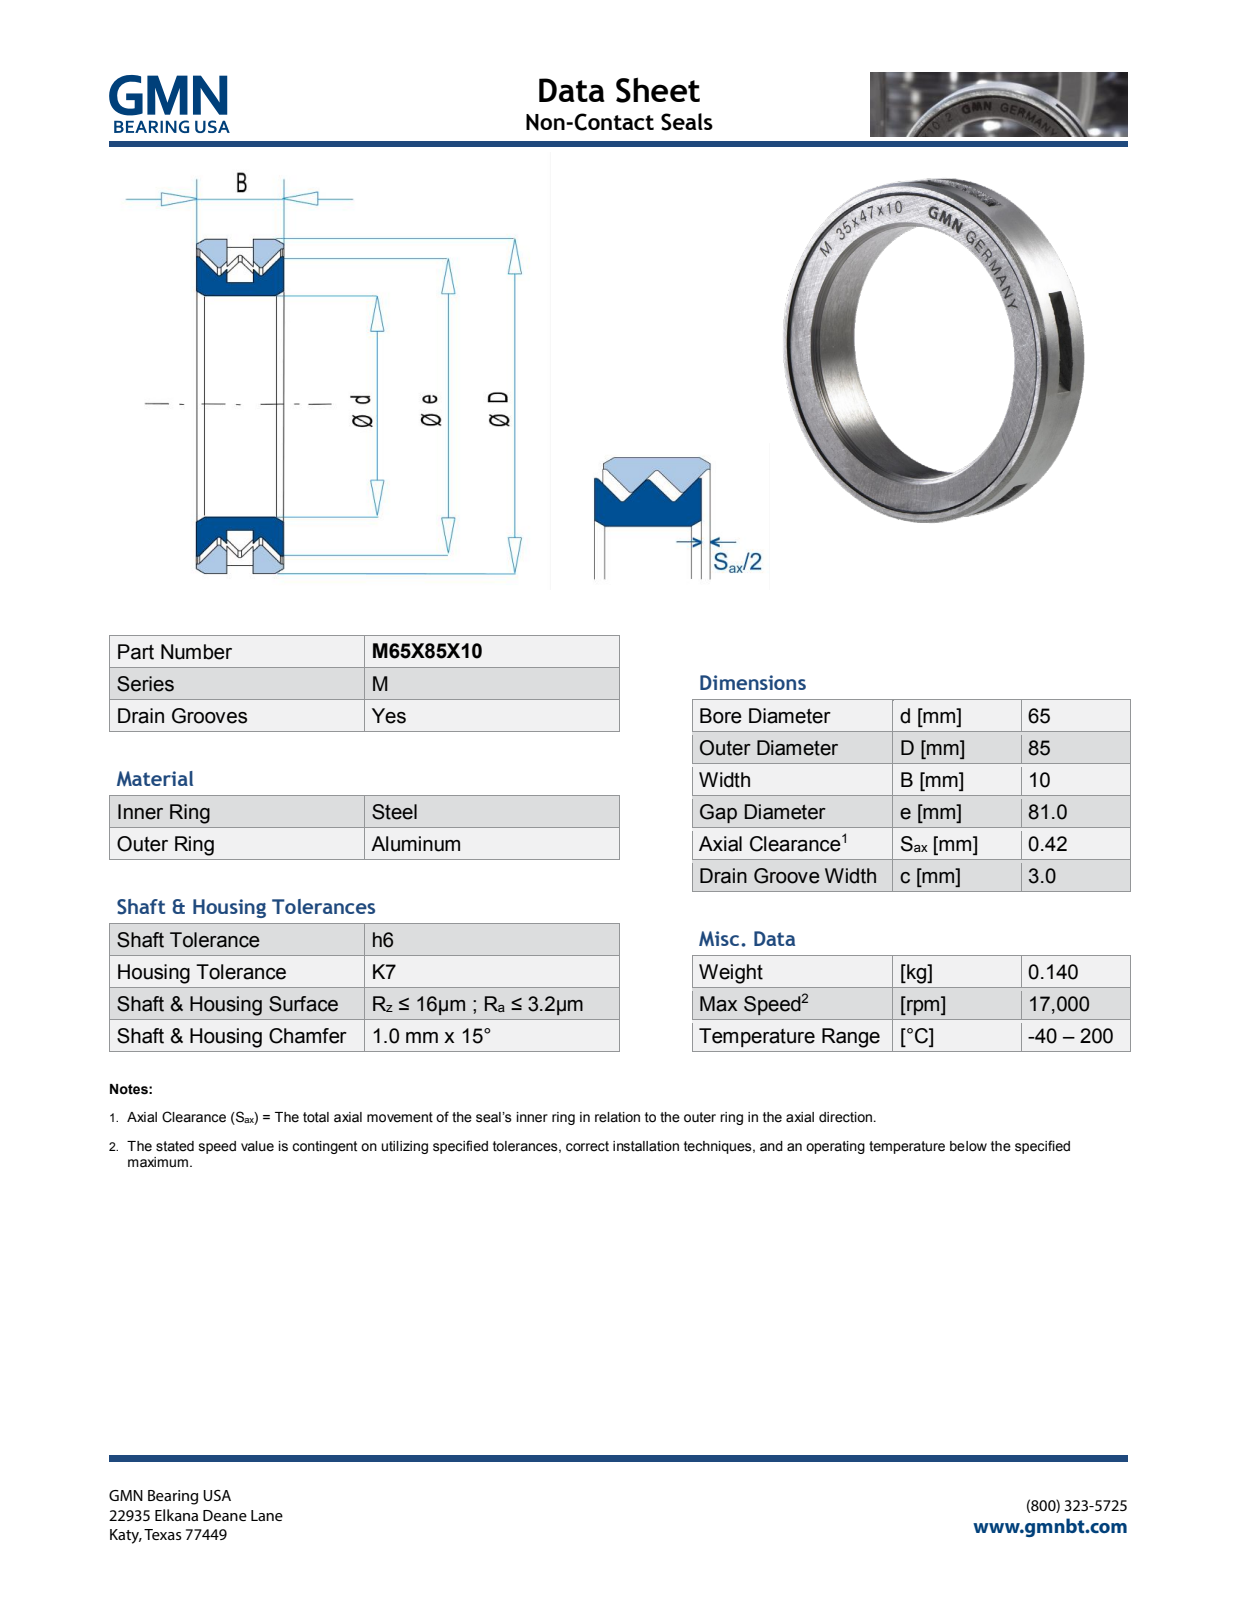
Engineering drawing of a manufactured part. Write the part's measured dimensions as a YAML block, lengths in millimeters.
part_name: "M65X85X10_PRT"
step_written_by: "PRO/ENGINEER BY PARAMETRIC TECHNOLOGY CORPORATION, 2013150 (AUTOMOTIVE_DESIGN)"
units: millimeters
bodies: {solids: 2, faces: 682, planar: 605, cylindrical: 27, other: 50}
overall_size: [85, 85, 10.07]
volume: 21874
surface_area: 15782
round_holes:
  - {diameter: 65, count: 1}
  - {diameter: 81.3, count: 1}
round_bosses_or_shafts:
  - {diameter: 85, count: 1}
  - {diameter: 81, count: 1}
partial_cylinders:
  - {radius: 10, count: 5}
face_to_face_distances: [10, 3.5, 6.5, 3, 3.57, 6.57, 10.07, 0.68, 5.42, 4.74]
